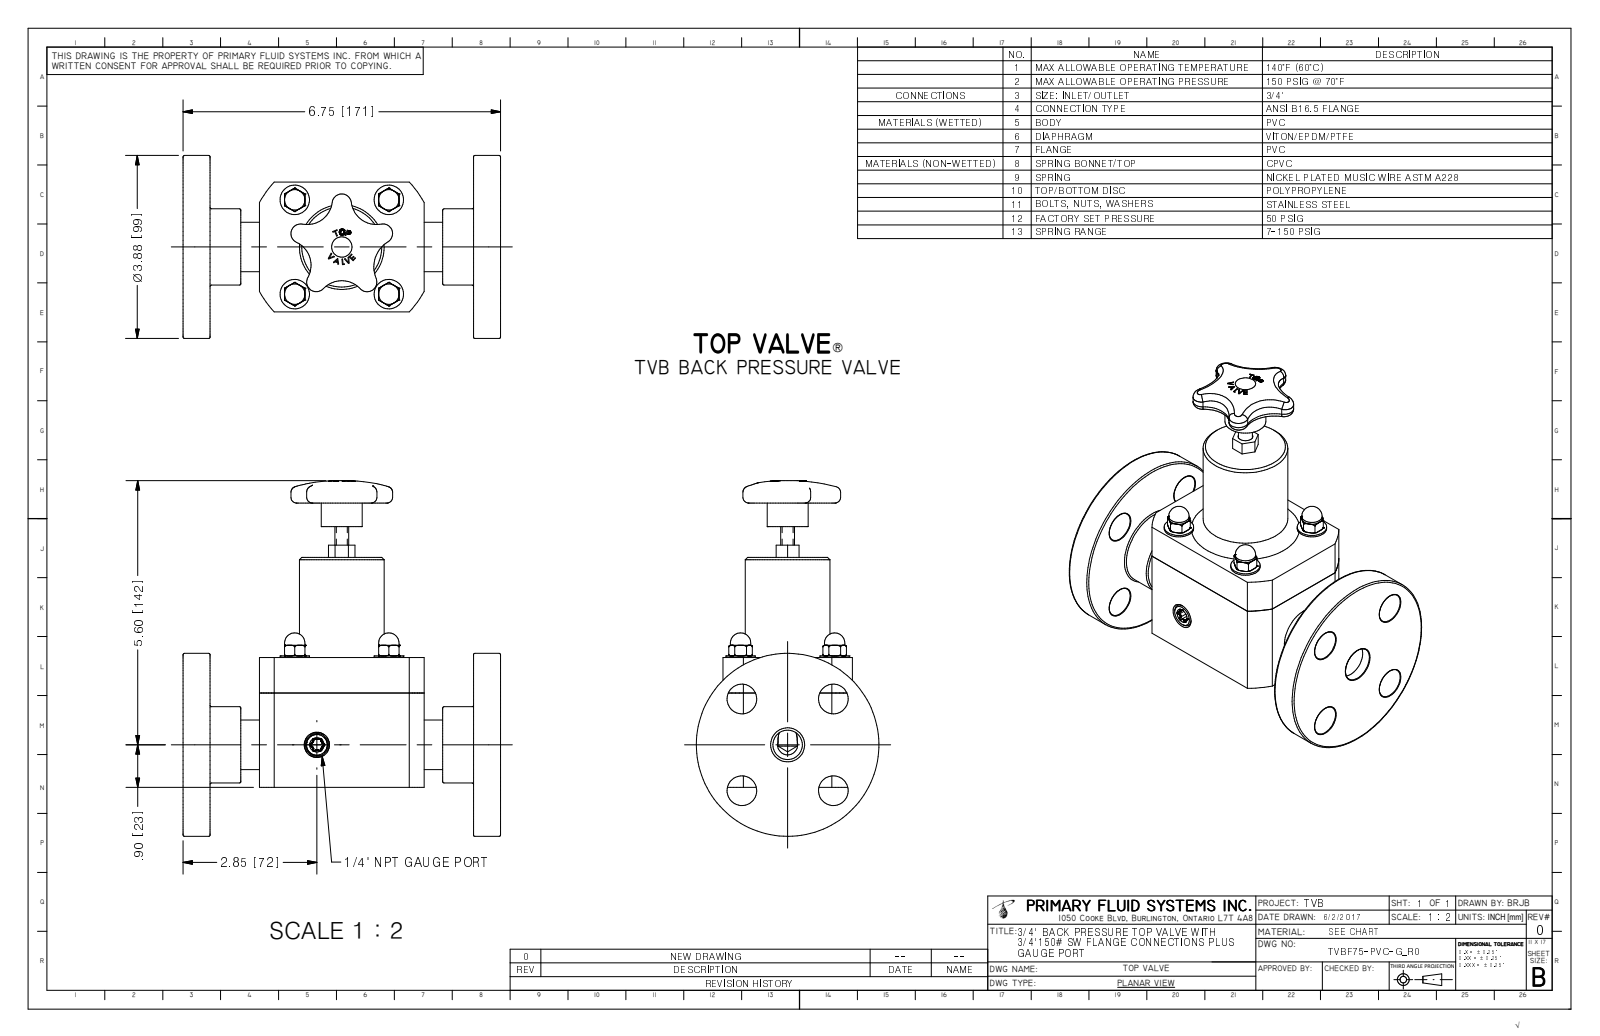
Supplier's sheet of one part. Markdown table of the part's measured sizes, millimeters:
| quantity | value |
| --- | --- |
| part name | TVBF75-PVC-G_R0 |
| STEP written by | Autodesk Inventor 2009 (AUTOMOTIVE_DESIGN) |
| units | millimeters |
| bodies | 1 solid, 415 faces (160 planar, 67 cylindrical, 188 other) |
| overall size | 191.6 × 171.5 × 98.6 |
| volume | 759 400 mm³ |
| surface area | 112 400 mm² |
| round holes (diameter × count) | 4.4 × 4, 16 × 4, 18.3 × 1, 18.8 × 1 |
| round bosses / shafts (diameter × count) | 15.9 × 4, 11 × 4, 9.5 × 4, 98.6 × 1, 45.7 × 1, 41 × 1, 26.7 × 1, 22.1 × 1 |
| partial cylindrical surfaces (radius × count) | 0.7 × 6, 2.2 × 5, 5.2 × 5, 13.6 × 4, 16.7 × 4, 15.9 × 1, 18.9 × 1, 50.5 × 1 |
| main face-to-face distances | 14.6, 156.8, 171.5, 41.3, 130.2, 26.7, 115.6, 142.2, 69.9, 88.9 |
| hole center spacings | 34.9, 49.4, 50.8, 69.9, 71.8 |
